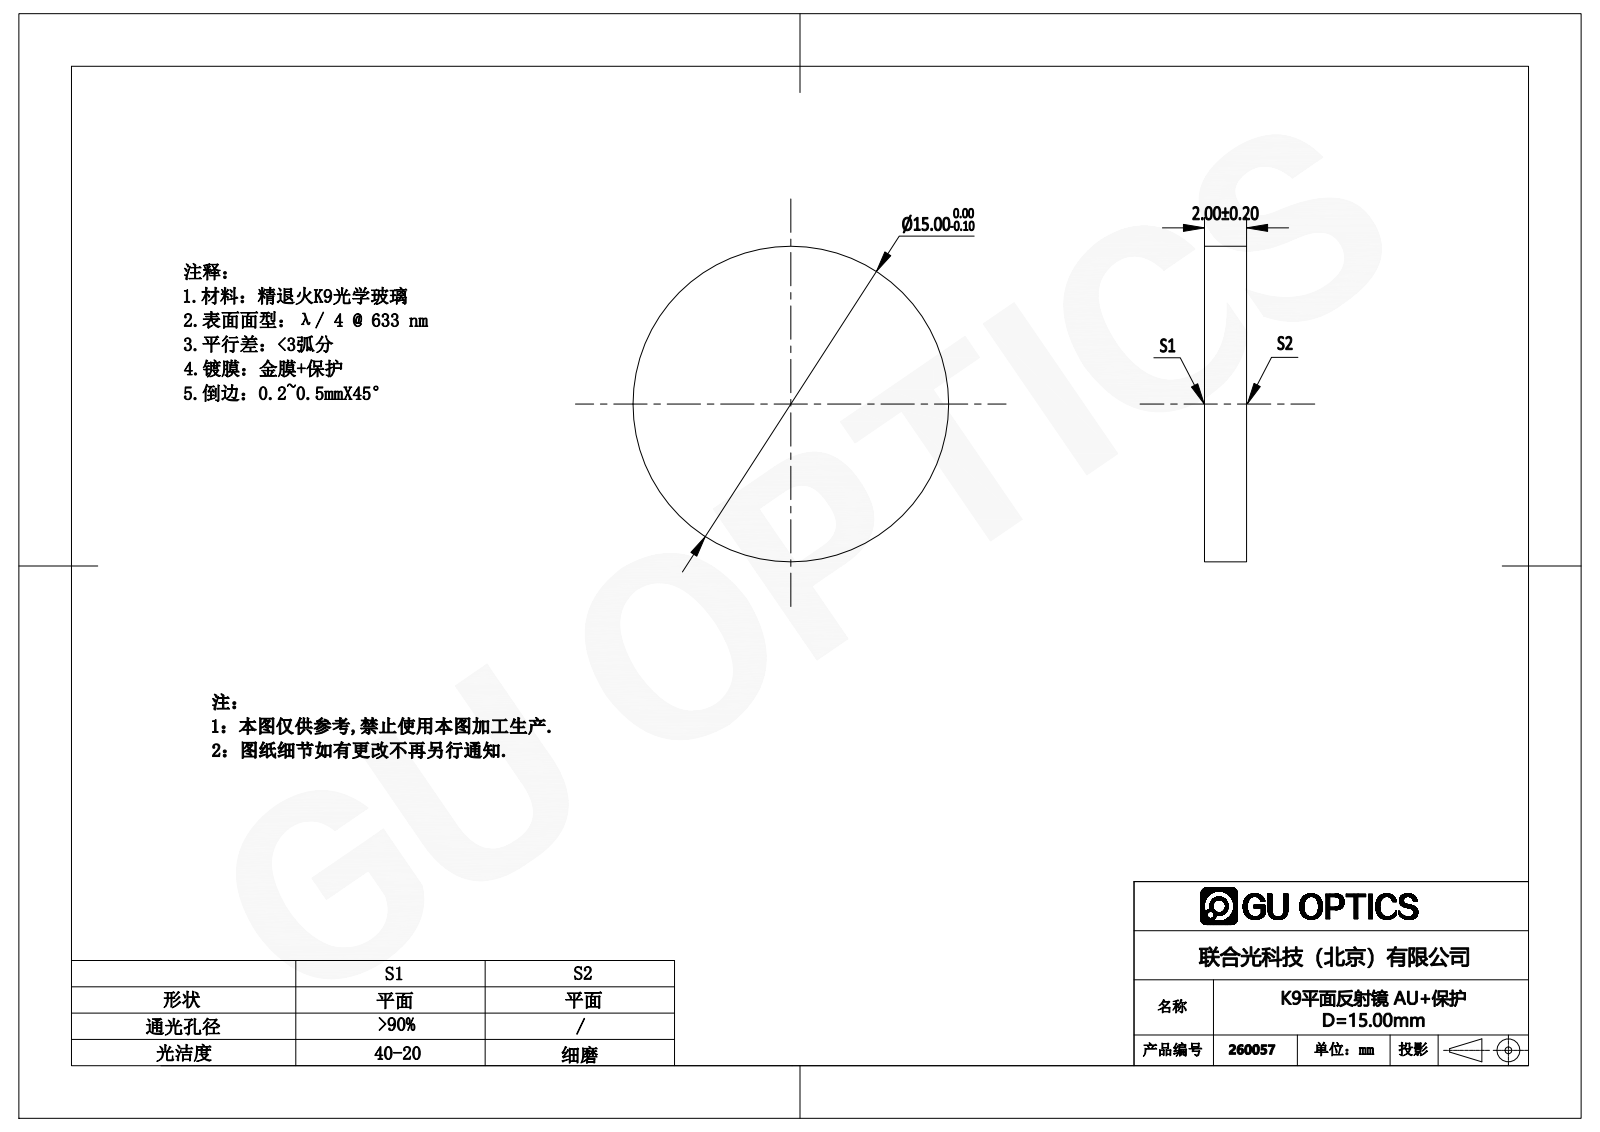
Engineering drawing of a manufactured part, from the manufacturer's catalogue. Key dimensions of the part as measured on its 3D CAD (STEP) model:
Part name (STEP PRODUCT): 260005
STEP written by: SolidWorks 2016 (AUTOMOTIVE_DESIGN)
Units: millimetres
Bodies: 1 solid, 4 faces (2 planar, 2 cylindrical, 0 other)
Overall size (bounding box): 15 × 15 × 2
Volume: 353 mm³ · Surface area: 448 mm²
Round bosses / shafts (diameter × count): ⌀15 ×1
Main face-to-face distances: 2
